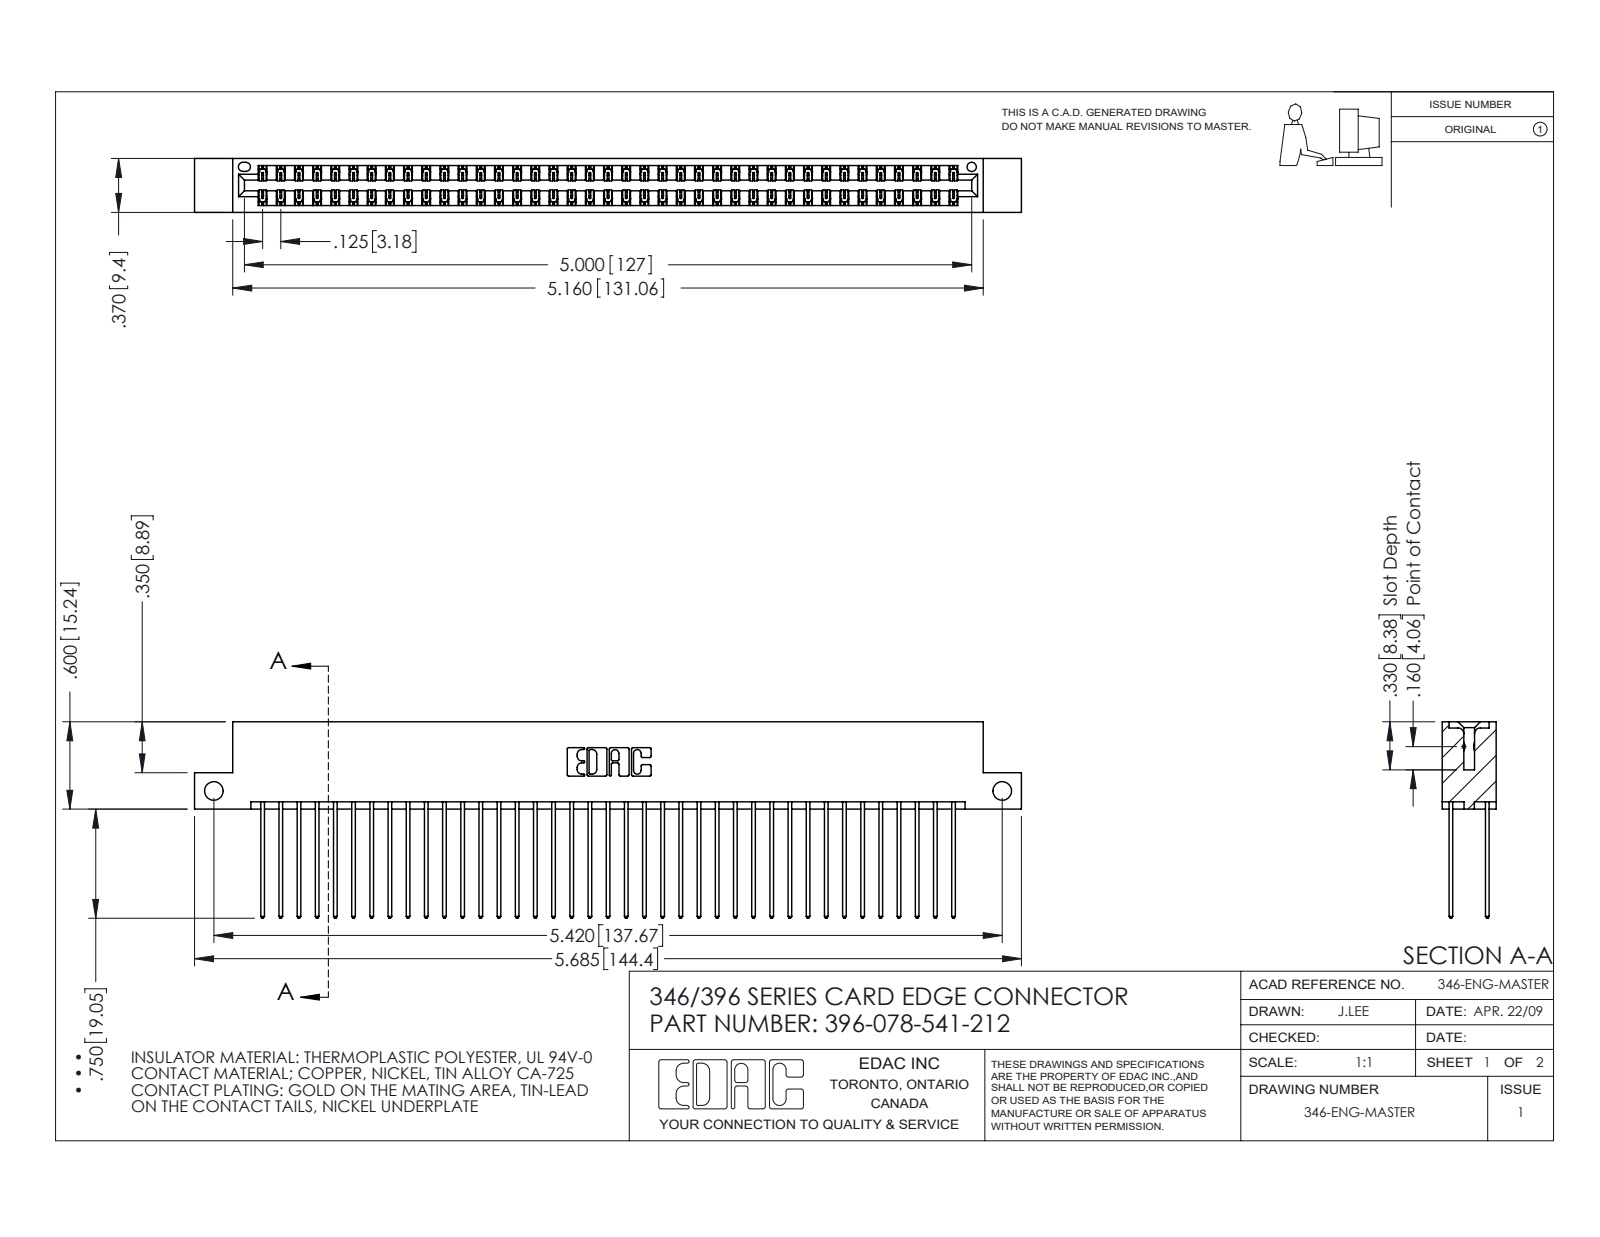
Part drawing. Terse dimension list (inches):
name: 396-078-541-212; 345-292-001_345-293-141; 346 Part_Flush Mounting Lugs - Side Mount
written by: SolidWorks 2016 (CONFIG_CONTROL_DESIGN)
unit: in
bodies: 79 solids, 4178 faces (2806 planar, 1372 cylindrical, 0 other)
size: 5.685 × 1.35 × 0.37
volume: 0.88 in³; area: 33.76 in²
holes: 2× ⌀0.128, 1× ⌀0.064
rounds: 117× R0.006, 78× R0.01, 22× R0.01, 6× R0.007, 6× R0.031, 3× R0.026, 2× R0.014, 2× R0.022
face distances: 0.048, 0.322, 0.25, 0.072, 0.298, 0.025, 0.37, 0.275, 0.225, 0.148
hole spacings: 5.42
